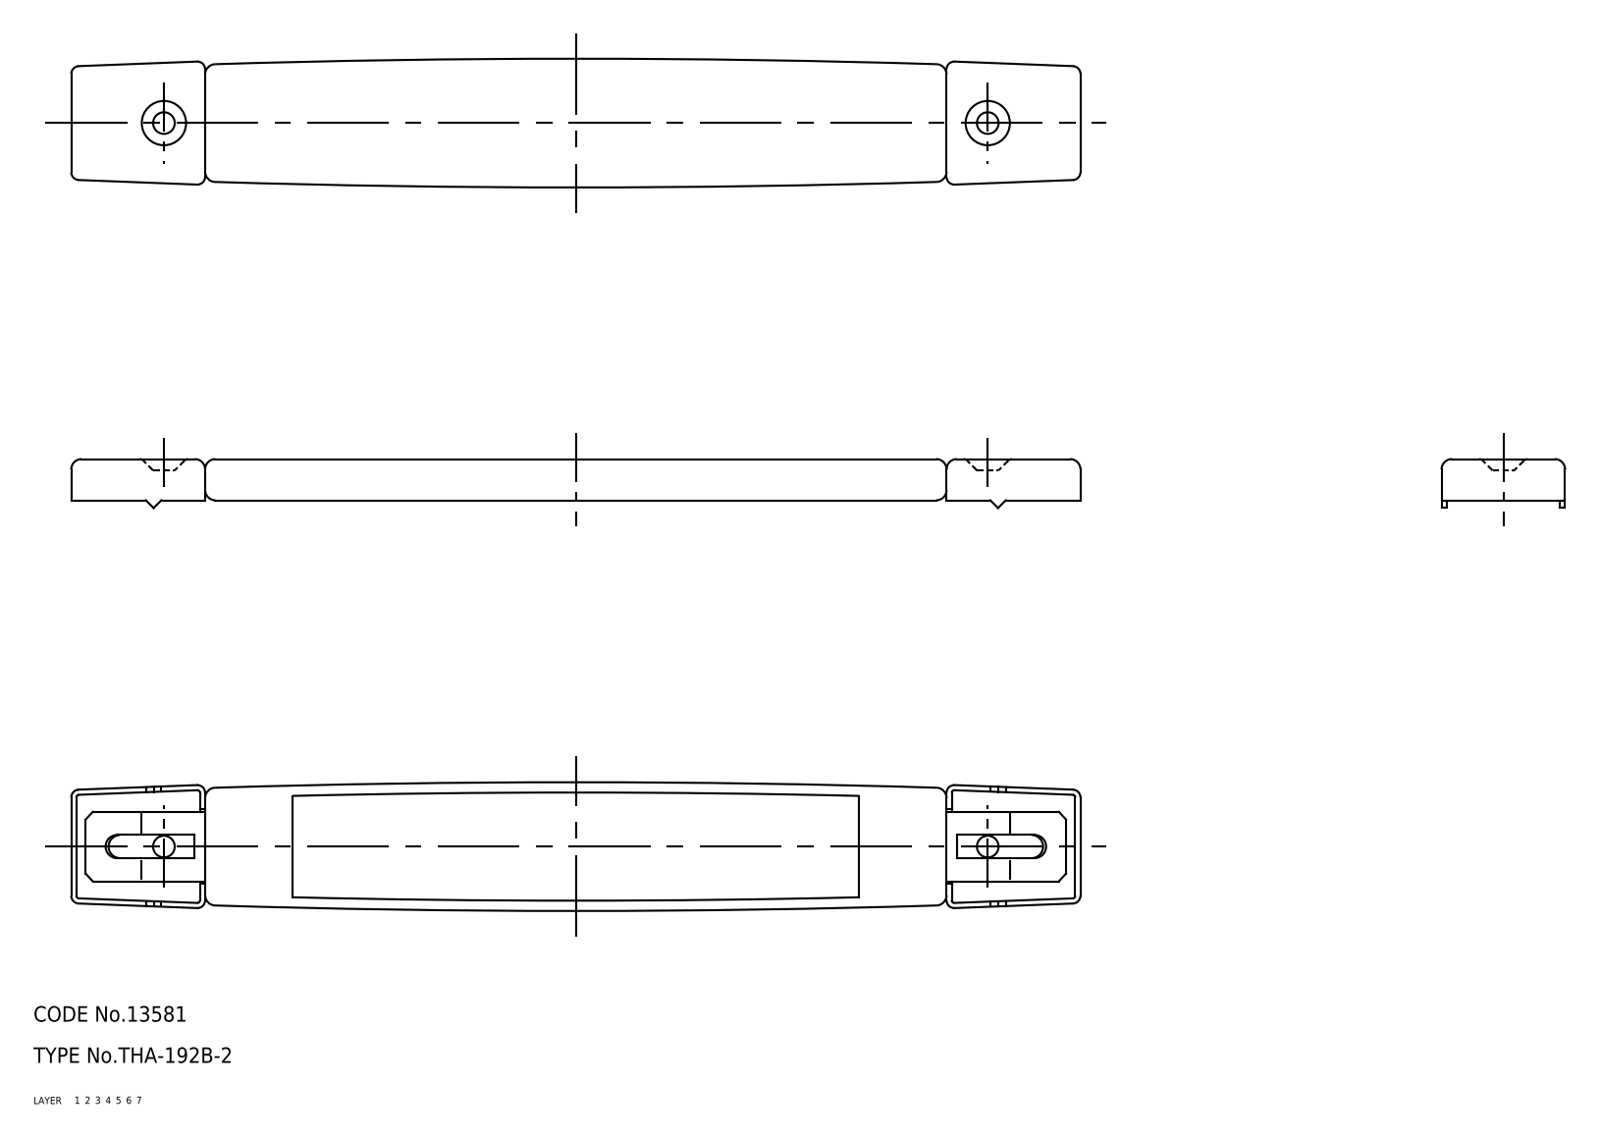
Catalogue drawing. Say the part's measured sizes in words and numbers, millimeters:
The part is named "67116146; 67116159; 67116172; 67116185 (+1 more)". Its 3-D file was written by "CADfix (AUTOMOTIVE_DESIGN)". It is 5 solids with 166 faces: 0 planar, 0 cylindrical and 166 other. Overall it measures 196 by 25 by 9.5 millimeters. Its volume is 27 856 cubic millimeters and its surface area 20 781 square millimeters.
